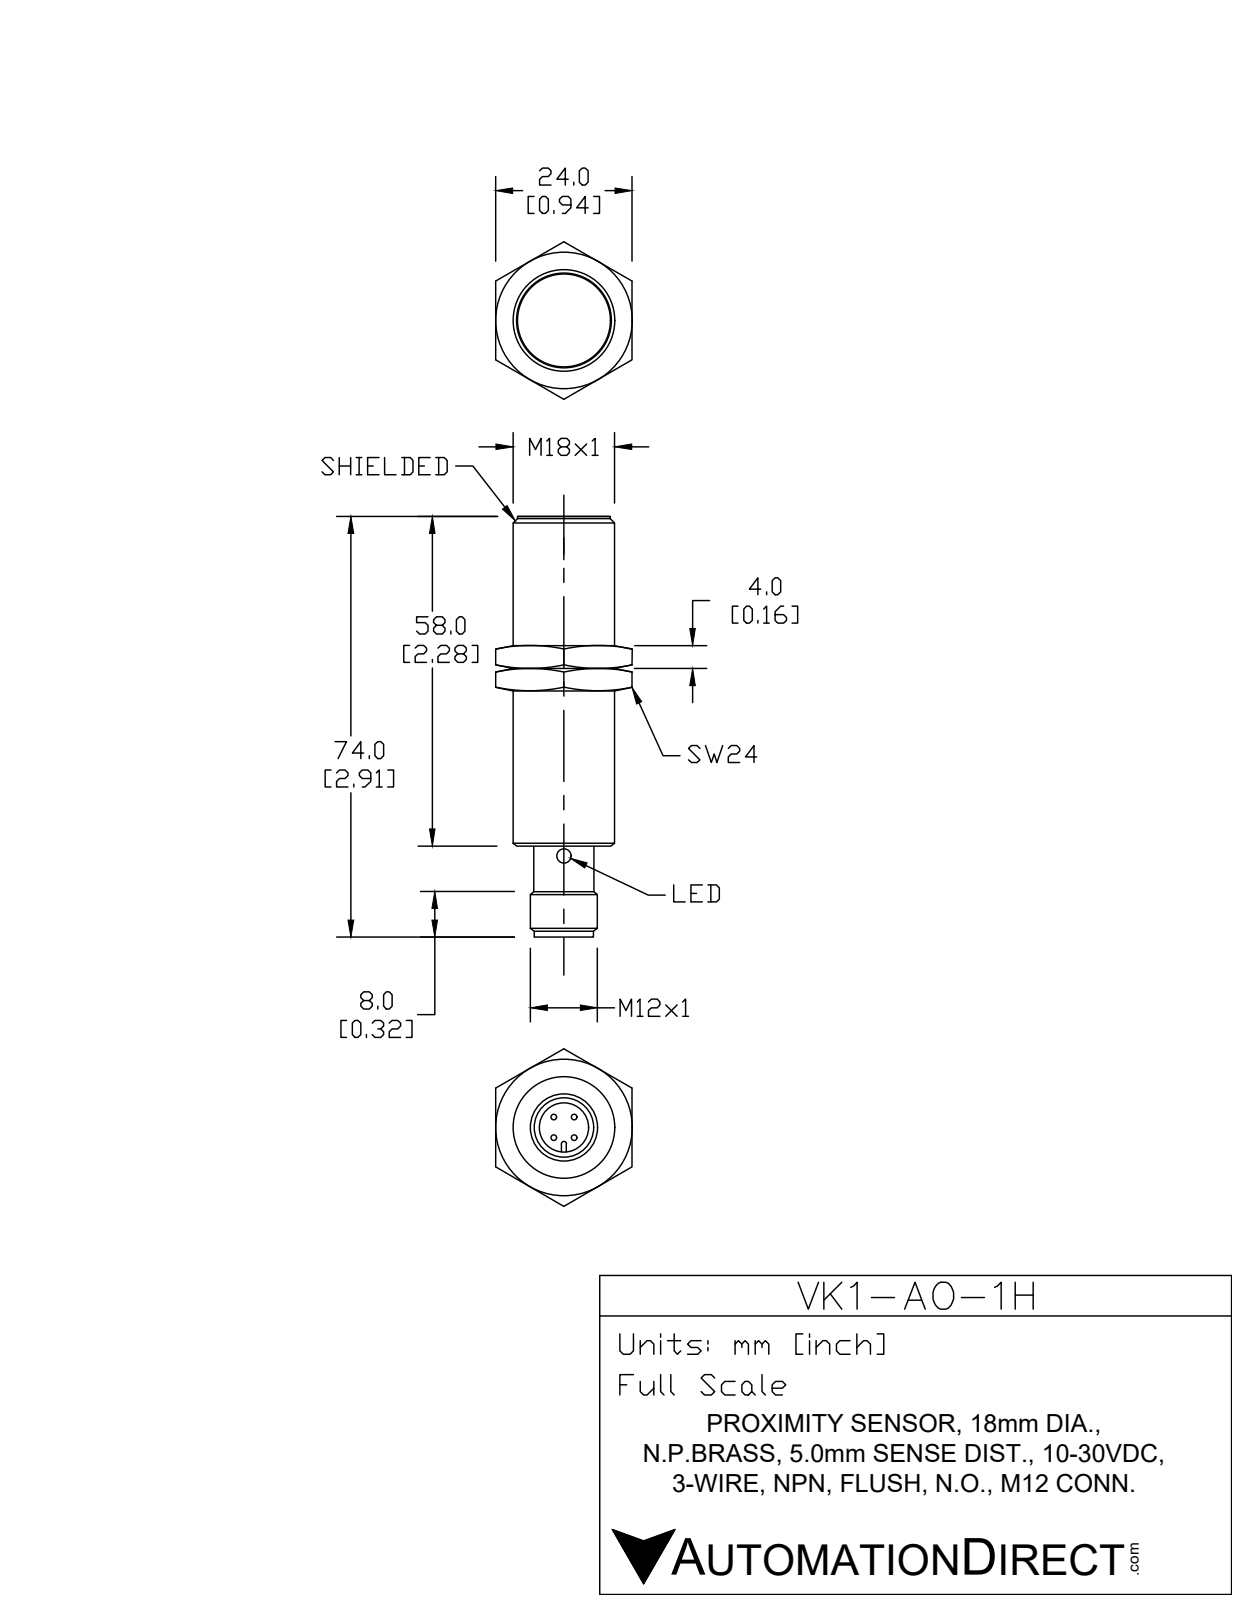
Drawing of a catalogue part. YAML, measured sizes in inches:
part_name: "VK1-A0-1H"
step_written_by: "SolidWorks 2017 (AUTOMOTIVE_DESIGN)"
units: inches
bodies: {solids: 4, faces: 120, planar: 24, cylindrical: 64, other: 32}
overall_size: [2.906, 0.709, 0.709]
volume: 0.956
surface_area: 9.777
round_holes:
  - {diameter: 0.098, count: 4}
  - {diameter: 0.331, count: 1}
round_bosses_or_shafts:
  - {diameter: 0.039, count: 4}
  - {diameter: 0.709, count: 1}
  - {diameter: 0.646, count: 1}
  - {diameter: 0.472, count: 1}
  - {diameter: 0.413, count: 1}
  - {diameter: 0.386, count: 1}
  - {diameter: 0.382, count: 1}
  - {diameter: 0.378, count: 1}
partial_cylinders:
  - {radius: 0.051, count: 4}
  - {radius: 0.02, count: 1}
  - {radius: 0.024, count: 1}
  - {radius: 0.051, count: 1}
  - {radius: 0.134, count: 1}
face_to_face_distances: [2.244, 0.02, 2.264, 2.283, 2.461, 2.441, 0.197, 0.177, 2.469, 2.449]
